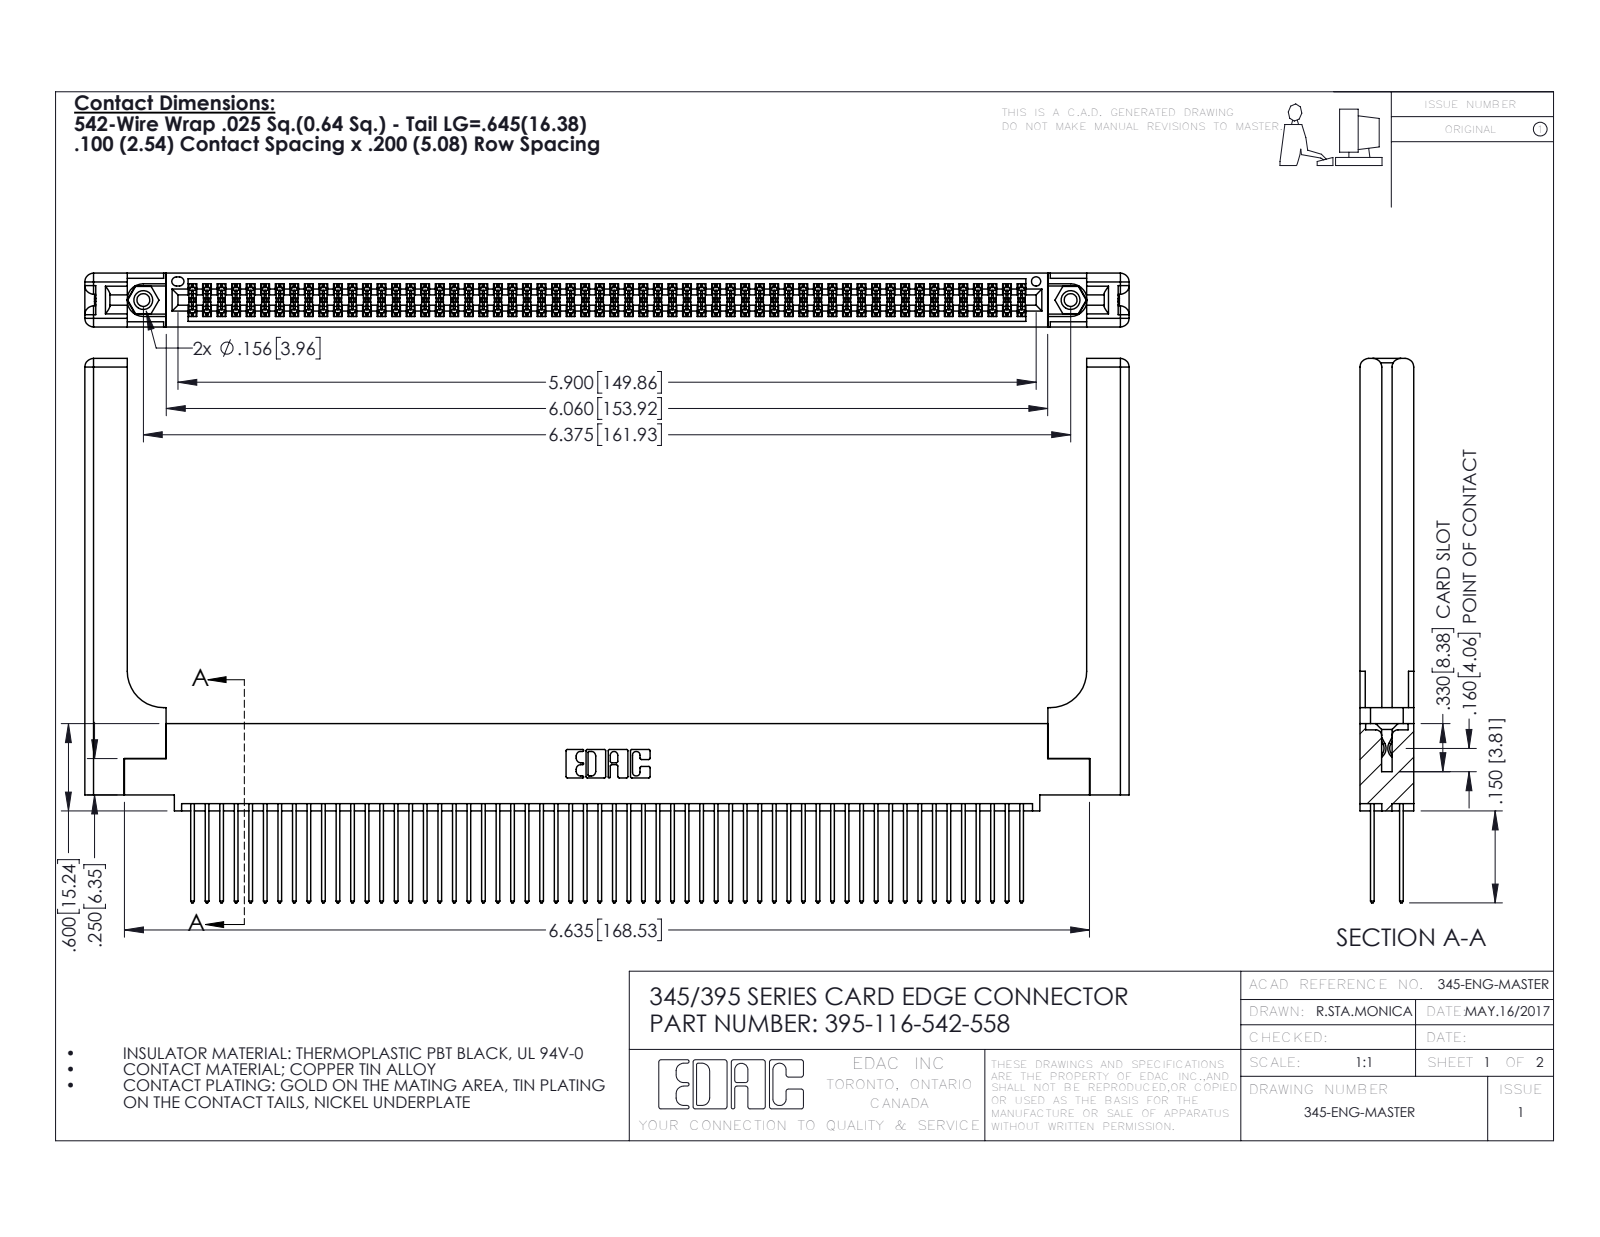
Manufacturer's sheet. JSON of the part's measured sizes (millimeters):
{"part_name": "395-116-542-558; 345-220-058_345-220-058; 345-250-001_345-250-001-102; 345-292-001_345-293-142 (+1 more)", "step_written_by": "SolidWorks 2016 (CONFIG_CONTROL_DESIGN)", "units": "millimeters", "bodies": {"solids": 121, "faces": 6186, "planar": 4060, "cylindrical": 2066, "other": 60}, "overall_size": [182.3, 95, 9.4], "volume_mm3": 26810, "surface_area_mm2": 35080, "round_holes": [[2.3, 2], [3.2, 2], [4, 2], [1.6, 1]], "round_bosses_or_shafts": [[3.9, 2]], "partial_cylinders_radius": [[0.2, 174], [0.3, 116], [0.3, 22], [1.5, 16], [0.2, 6], [0.8, 6], [0.7, 3], [0.4, 2]], "face_to_face_distances": [1.8, 7.6, 9.4, 2.5, 6.9, 0.6, 5.1, 5.7, 4.4, 3.8], "hole_center_spacings": [6.9, 155.9, 161.9]}
